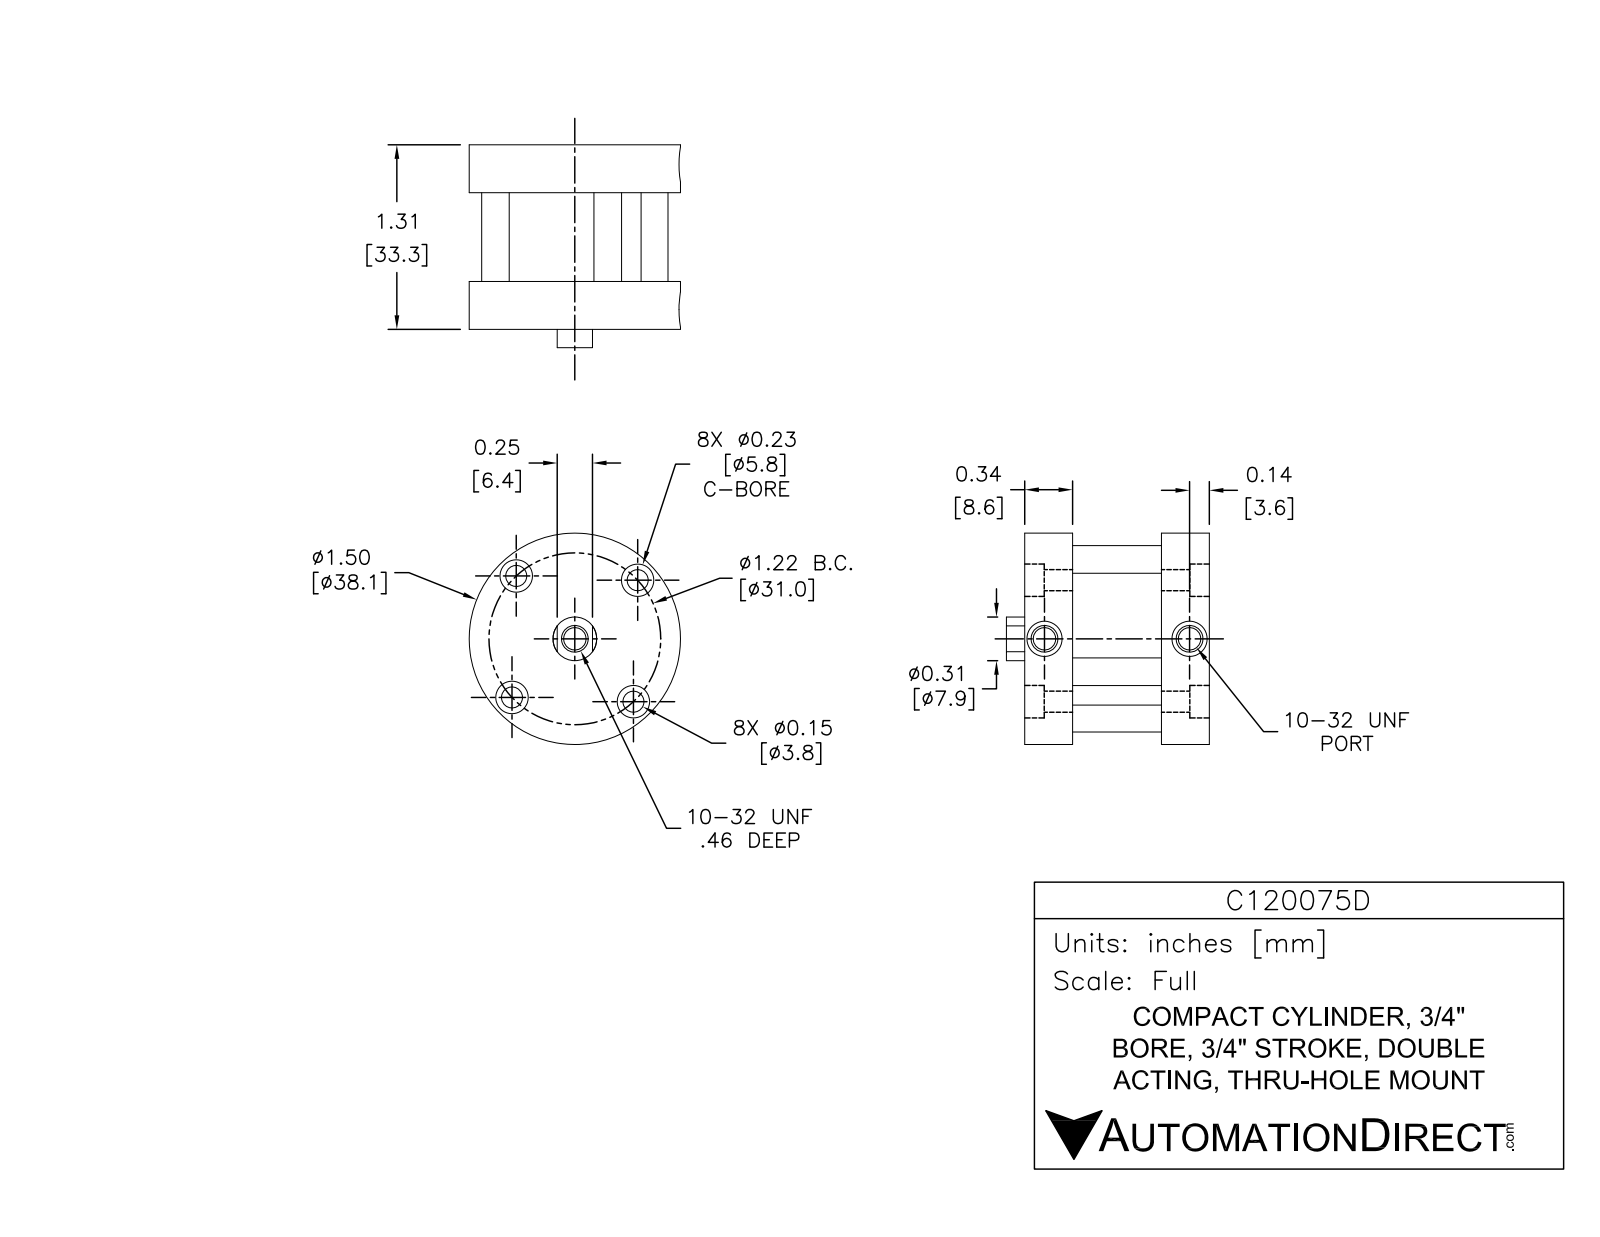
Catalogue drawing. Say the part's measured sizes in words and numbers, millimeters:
The part is named "C120075D-rod_part; C120075D-FO1_BM_r; C120075D-FO1_BM_rod; C120075D-FO1_BM_heads (2) (+3 more)". Its 3-D file was written by "SolidWorks 2014 (AUTOMOTIVE_DESIGN)". It is 9 solids with 165 faces: 51 planar, 104 cylindrical and 10 other. Overall it measures 38.1 by 38.1 by 36.6 millimeters. Its volume is 21 320 cubic millimeters and its surface area 15 850 square millimeters. Round holes: 4 of diameter 3.5, 4 of diameter 4, 4 of diameter 6, 3 of diameter 4, 2 of diameter 8, 1 of diameter 7.9, 1 of diameter 7.9, 1 of diameter 19.1, 1 of diameter 20.6. Round bosses or shafts: 4 of diameter 6.9, 1 of diameter 38.1. The main face-to-face distances are 4.3, 24.6, 20.3, 33.3, 8.6, 8.6, 16, 24.6, 29, 29. The hole center spacings are 15.5, 21.9, 8.4, 15.1, 27.1, 29.8, 31, 26.2.
